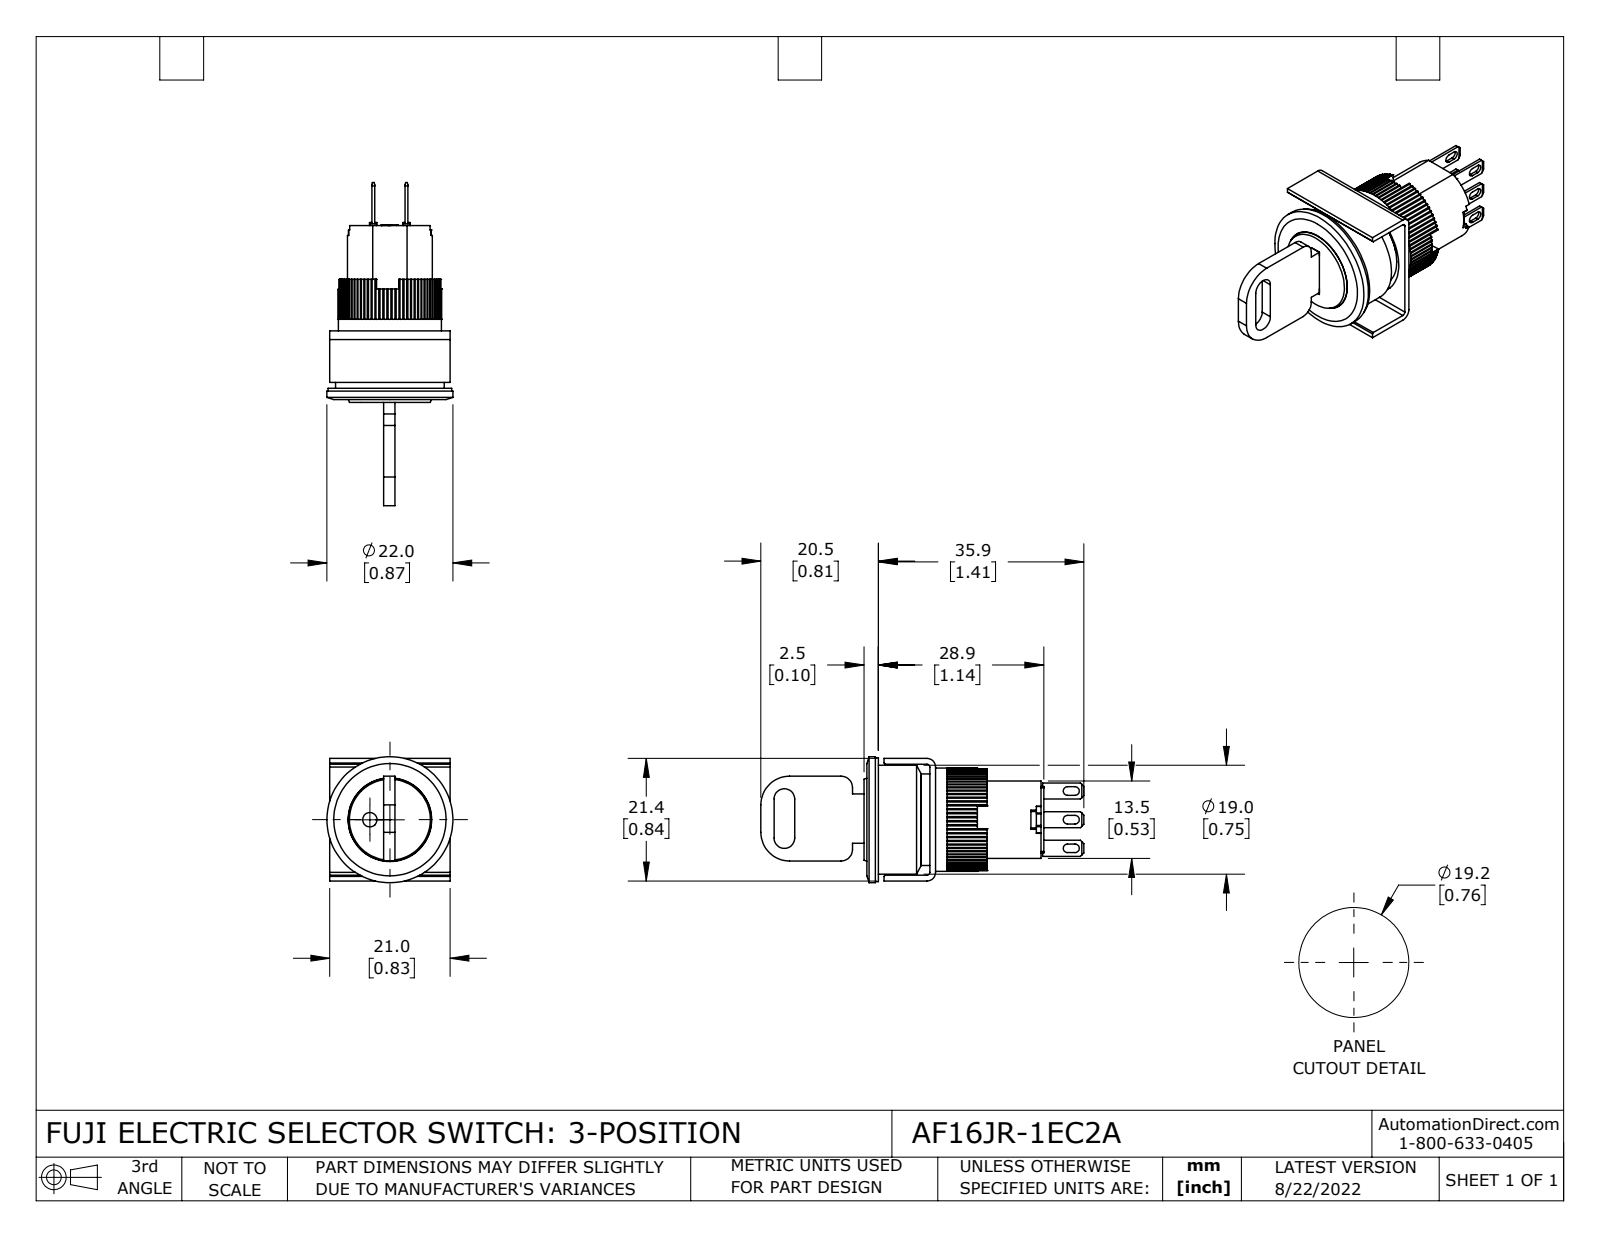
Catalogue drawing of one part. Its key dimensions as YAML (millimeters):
part_name: "AF16JR-1EC2A"
step_written_by: "SolidWorks 2021 (CONFIG_CONTROL_DESIGN)"
units: millimeters
bodies: {solids: 13, faces: 707, planar: 518, cylindrical: 183, other: 6}
overall_size: [56.4, 22, 22]
volume: 8110
surface_area: 7252
round_holes:
  - {diameter: 1, count: 1}
  - {diameter: 2.5, count: 1}
  - {diameter: 14.6, count: 1}
  - {diameter: 18, count: 1}
  - {diameter: 19, count: 1}
round_bosses_or_shafts:
  - {diameter: 22, count: 1}
  - {diameter: 21.6, count: 1}
  - {diameter: 16, count: 1}
  - {diameter: 14.8, count: 1}
  - {diameter: 14.5, count: 1}
partial_cylinders:
  - {radius: 0.3, count: 80}
  - {radius: 0.2, count: 12}
  - {radius: 0.8, count: 6}
  - {radius: 0.5, count: 2}
  - {radius: 1.5, count: 2}
  - {radius: 1.8, count: 2}
  - {radius: 2, count: 2}
  - {radius: 5, count: 2}
face_to_face_distances: [2, 1, 0.5, 9.5, 4.5, 2.5, 10, 20.4, 1.5, 19.4]
hole_center_spacings: [3.5]
